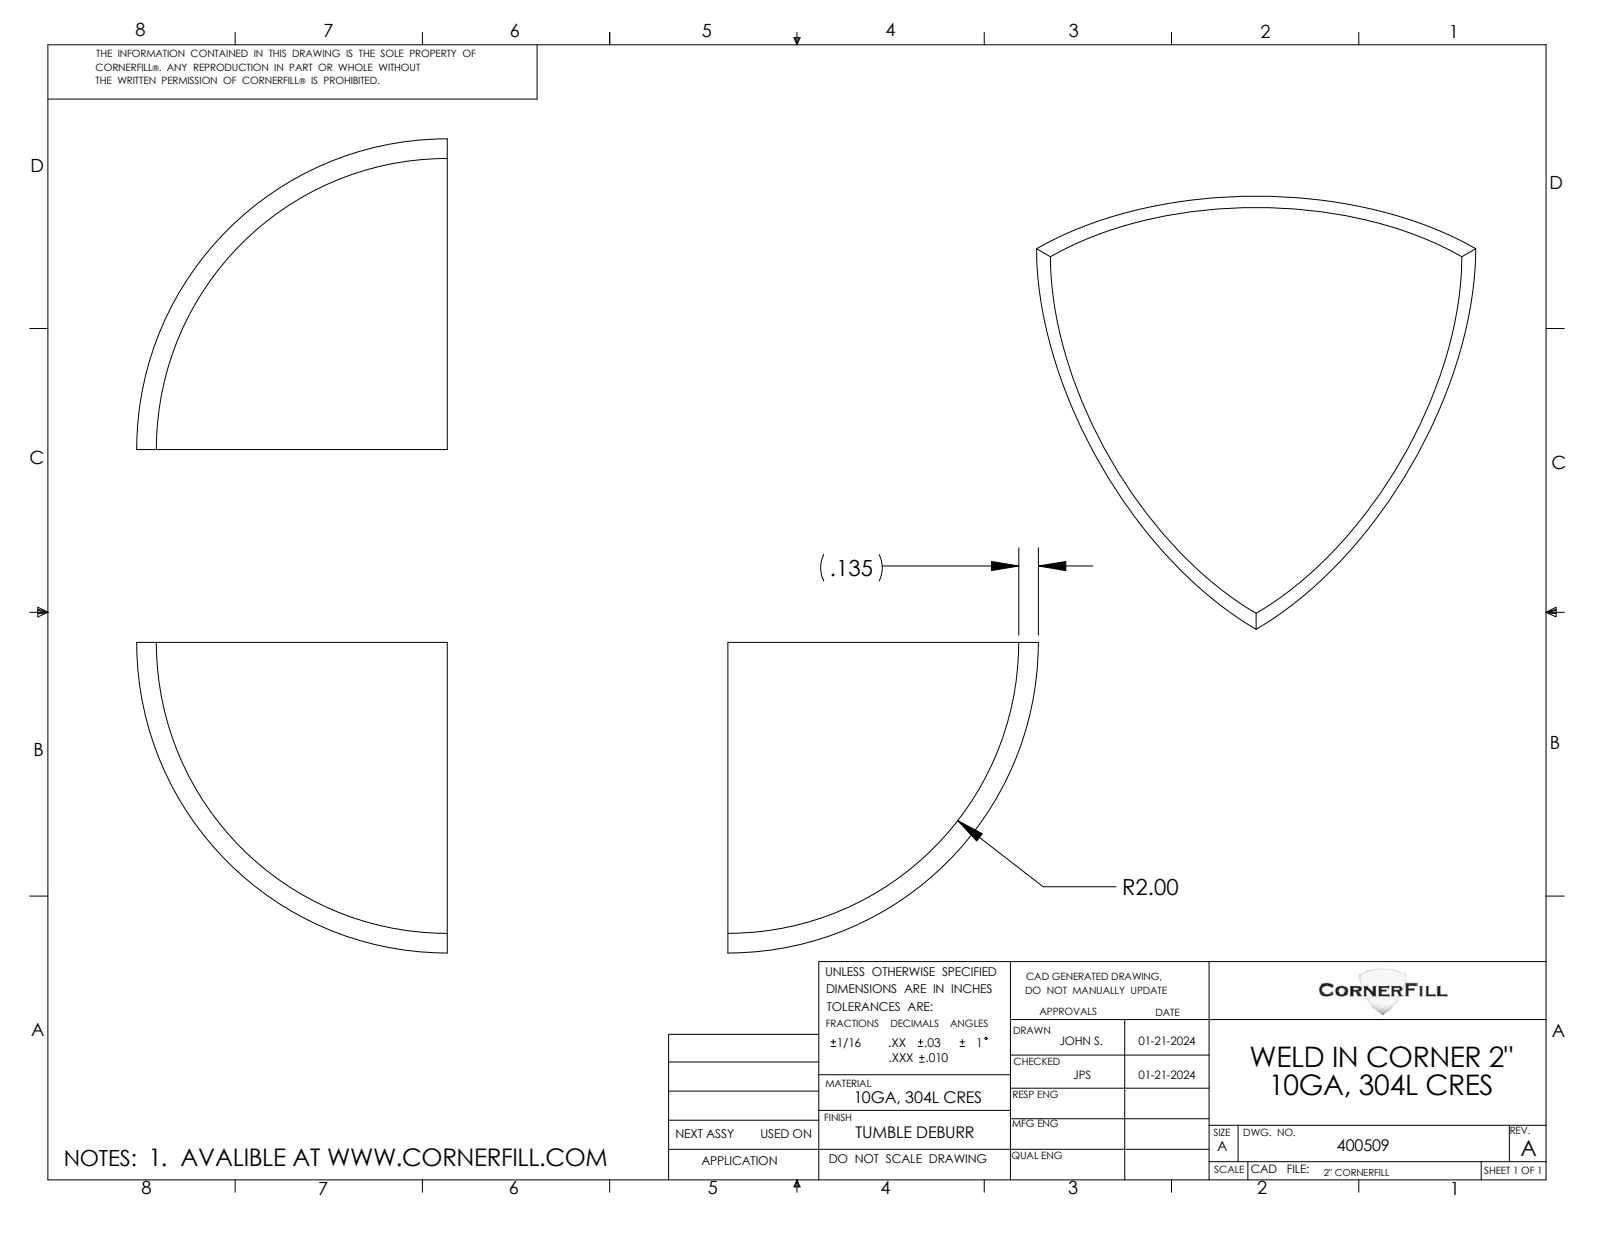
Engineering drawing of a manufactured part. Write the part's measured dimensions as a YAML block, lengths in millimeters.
part_name: "400509"
step_written_by: "SolidWorks 2021 (CONFIG_CONTROL_DESIGN)"
units: millimeters
bodies: {solids: 1, faces: 5, planar: 3, cylindrical: 0, other: 2}
overall_size: [76.7, 54.2, 54.2]
volume: 14900
surface_area: 9523
